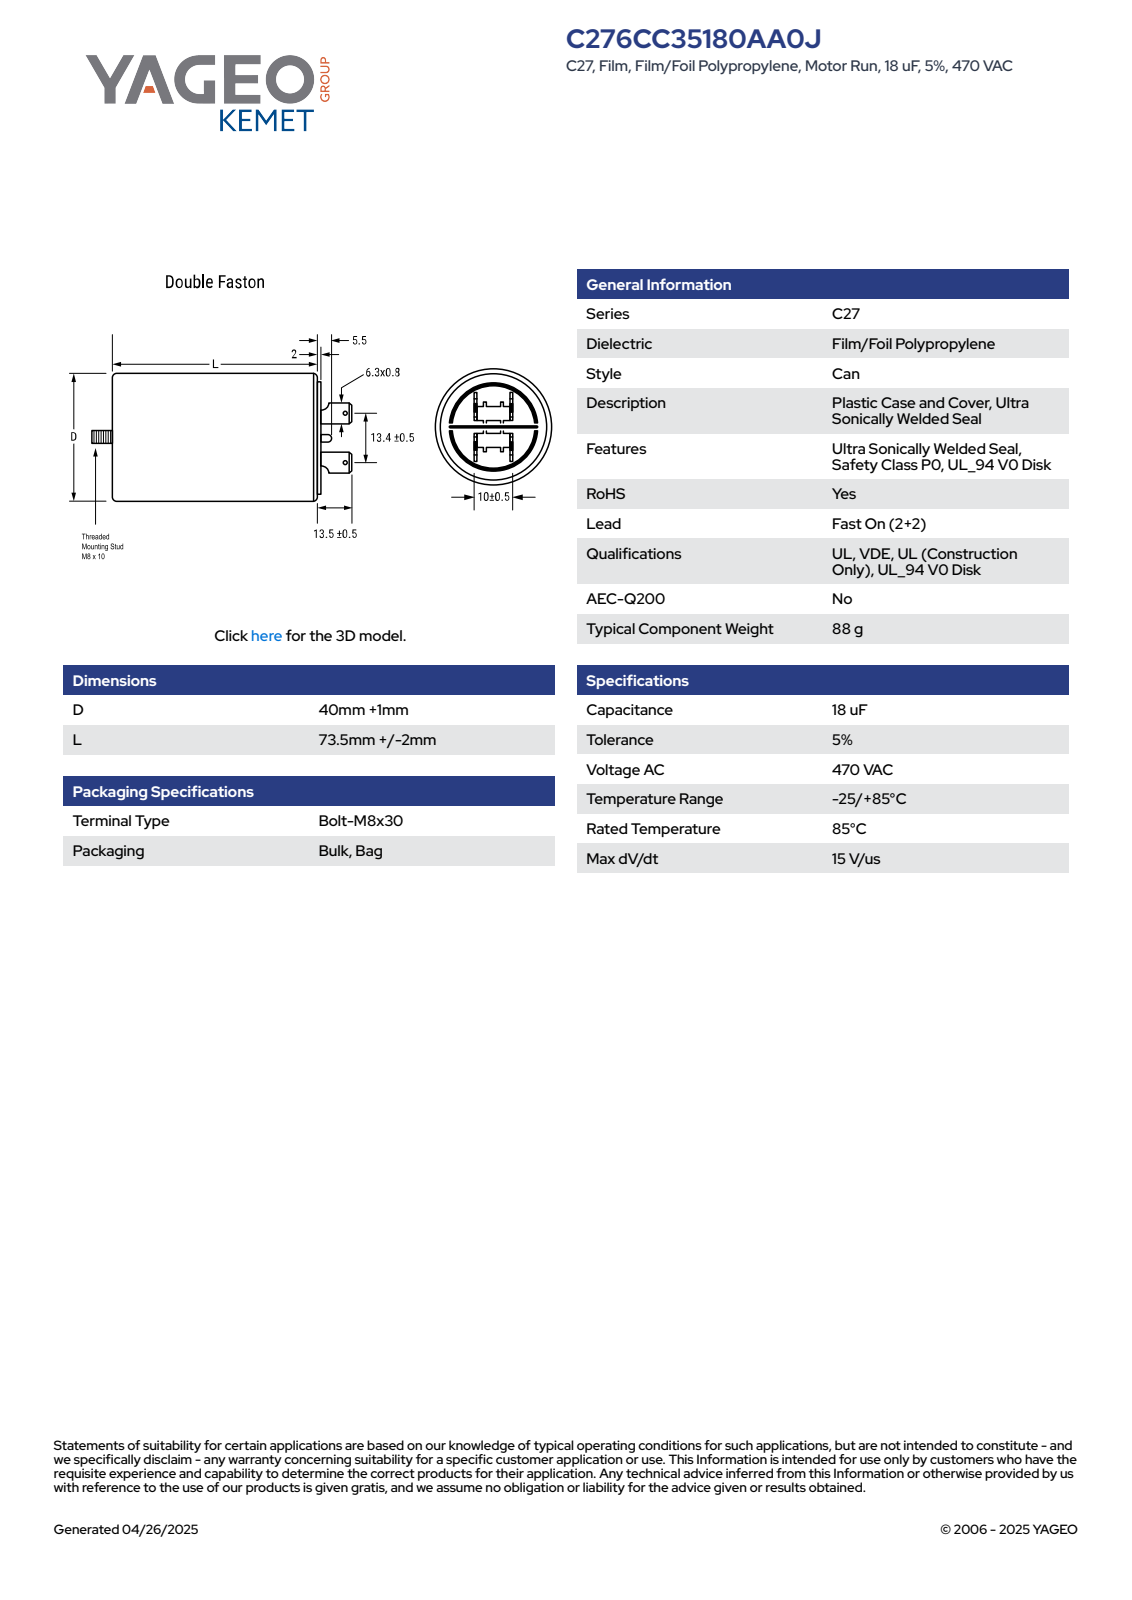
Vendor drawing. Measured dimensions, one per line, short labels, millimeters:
name: CFM_C27DF_40X73.5_D41L75.5
written by: SolidWorks 2014 (AUTOMOTIVE_DESIGN)
unit: mm
bodies: 1 solid, 137 faces (49 planar, 53 cylindrical, 35 other)
size: 99.5 × 41 × 41
volume: 101 806 mm³; area: 13 464 mm²
holes: 2× ⌀1.2
bosses: 1× ⌀41, 1× ⌀31.54, 1× ⌀8
rounds: 9× R0.25, 2× R4, 1× R20.49
face distances: 77.5, 75.5, 2, 0.8, 9.7, 10.5, 8.9, 0.5, 10, 85.5
hole spacings: 13.9
